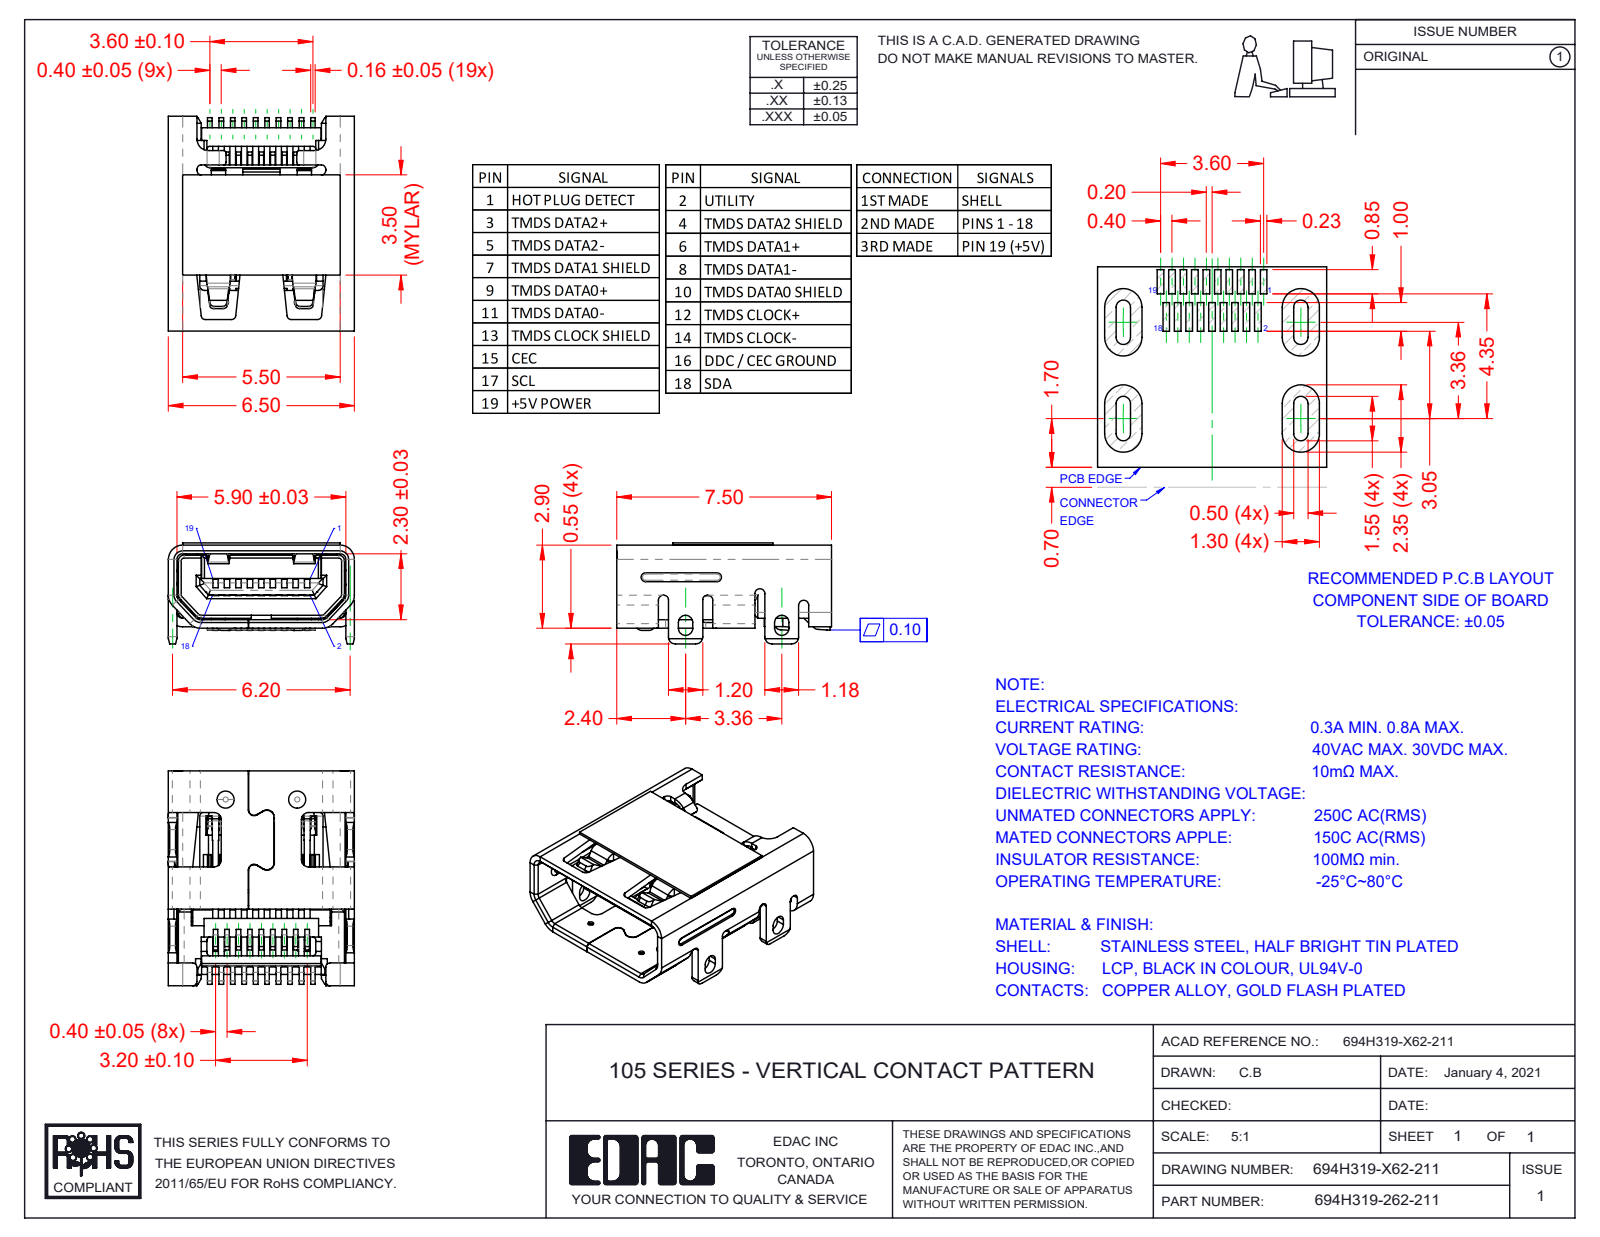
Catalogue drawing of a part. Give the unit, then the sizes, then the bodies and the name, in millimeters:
Units: millimetres
Overall size (bounding box): 7.5 × 6.5 × 3.53
Round holes (diameter × count): ⌀0.2 ×2
Partial cylindrical surfaces — rounded edges, fillets, slot ends (radius × count): R0.15 ×31, R0.2 ×18, R0.25 ×14, R0.1 ×8, R0.5 ×8, R0.16 ×6, R0.35 ×6, R0.24 ×3
Main face-to-face distances: 2.6, 0.35, 2.3, 6.2, 2.9, 0.65, 0.38, 2.68, 2.98, 0.5
Hole centre spacings: 2.5
Volume: 62 mm³ · Surface area: 457 mm²
Bodies: 3 solids, 1440 faces (1147 planar, 218 cylindrical, 75 other)
Part name (STEP PRODUCT): Insulator 694H319-X62-211; Tape 694H319-X62-211; Shell 694H319-X62-211; 694H319-162-211
STEP written by: SolidWorks 2020 (AUTOMOTIVE_DESIGN)
